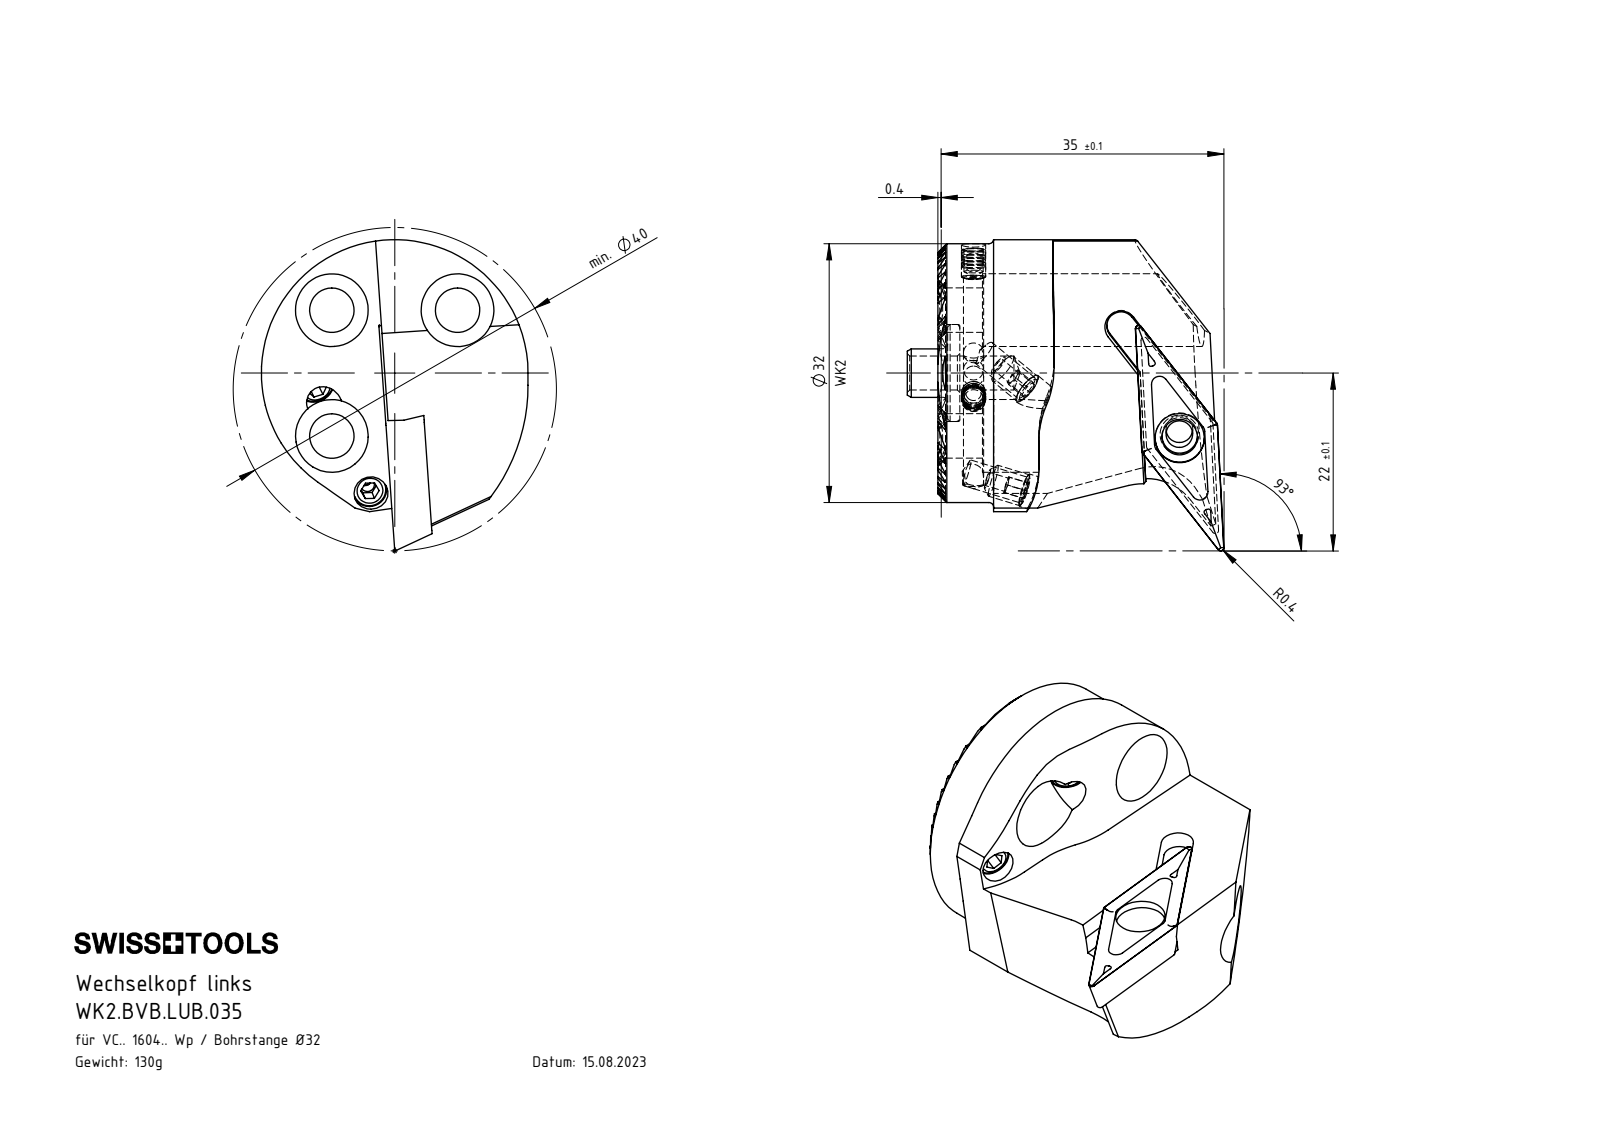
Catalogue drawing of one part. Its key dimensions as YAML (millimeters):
part_name: "WK2-ER1.001.012_A_Fertigbearbeitung; KVT_MB_600_030; VCMT160404; WK2-BVB.LUB.035_A (+2 more)"
step_written_by: "SolidWorks 2017 (AUTOMOTIVE_DESIGN)"
units: millimeters
bodies: {solids: 9, faces: 496, planar: 195, cylindrical: 164, other: 137}
overall_size: [39.2, 38.5, 33]
volume: 16057
surface_area: 8540
round_holes:
  - {diameter: 3.3, count: 3}
  - {diameter: 4.2, count: 3}
  - {diameter: 5.5, count: 3}
  - {diameter: 9, count: 3}
  - {diameter: 1.7, count: 2}
  - {diameter: 2.38, count: 2}
  - {diameter: 2.5, count: 2}
  - {diameter: 3, count: 2}
  - {diameter: 4.4, count: 1}
  - {diameter: 6.1, count: 1}
  - {diameter: 12, count: 1}
round_bosses_or_shafts:
  - {diameter: 4, count: 2}
  - {diameter: 3, count: 2}
  - {diameter: 32, count: 1}
  - {diameter: 6, count: 1}
partial_cylinders:
  - {radius: 0.12, count: 22}
  - {radius: 12, count: 3}
  - {radius: 1.75, count: 1}
  - {radius: 7, count: 1}
  - {radius: 16.5, count: 1}
  - {radius: 23, count: 1}
face_to_face_distances: [1.3, 2.6, 3.9, 5.2, 6.5, 12.99, 11.69, 14.29, 7.8, 10.39]
hole_center_spacings: [11, 15.56, 22.01]
